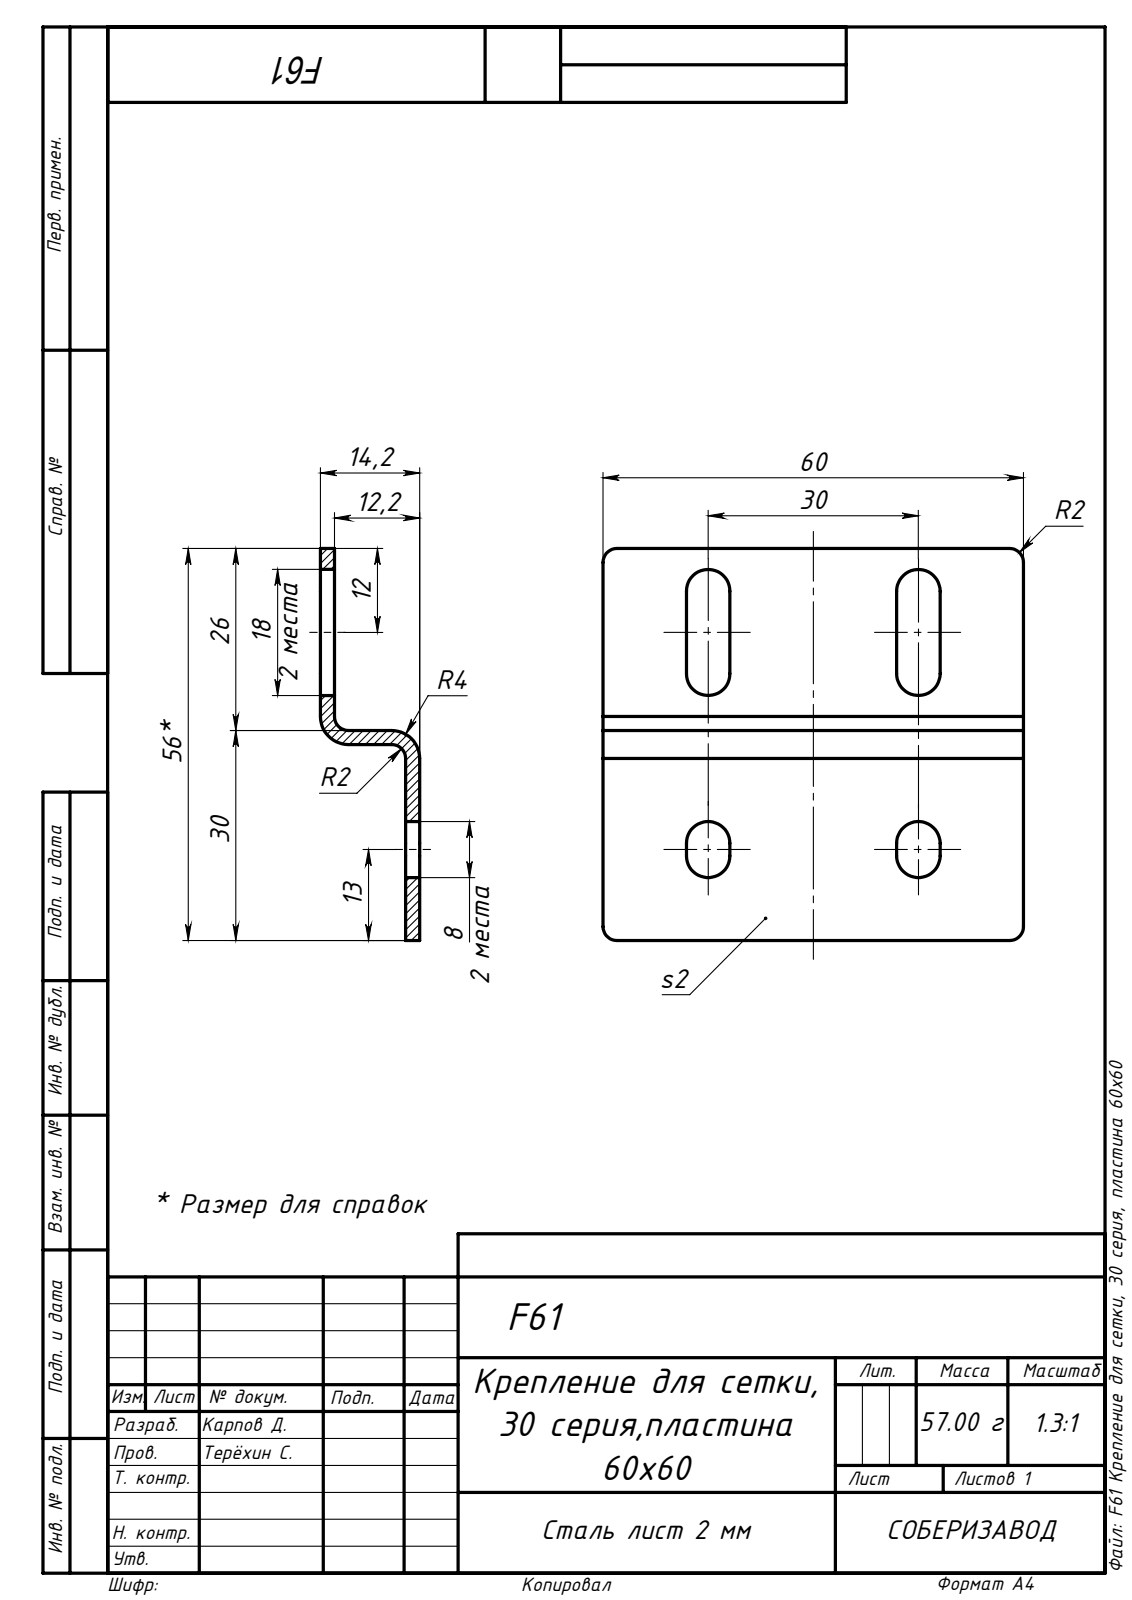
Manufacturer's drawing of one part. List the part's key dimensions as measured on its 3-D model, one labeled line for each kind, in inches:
Part name (STEP PRODUCT): F61 Крепление для сетки, 30 серия, пластина 60х60
STEP written by: SolidWorks 2020 (AUTOMOTIVE_DESIGN)
Units: inches
Bodies: 1 solid, 46 faces (26 planar, 20 cylindrical, 0 other)
Overall size (bounding box): 2.362 × 2.205 × 0.558
Volume: 0.445 in³ · Surface area: 12.47 in²
Partial cylindrical surfaces — rounded edges, fillets, slot ends (radius × count): R0.122 ×8, R0.079 ×6, R0.157 ×2
Main face-to-face distances: 0.079, 0.479, 0.558, 0.4, 1.102, 1.181, 2.362, 2.205, 1.024, 0.469
